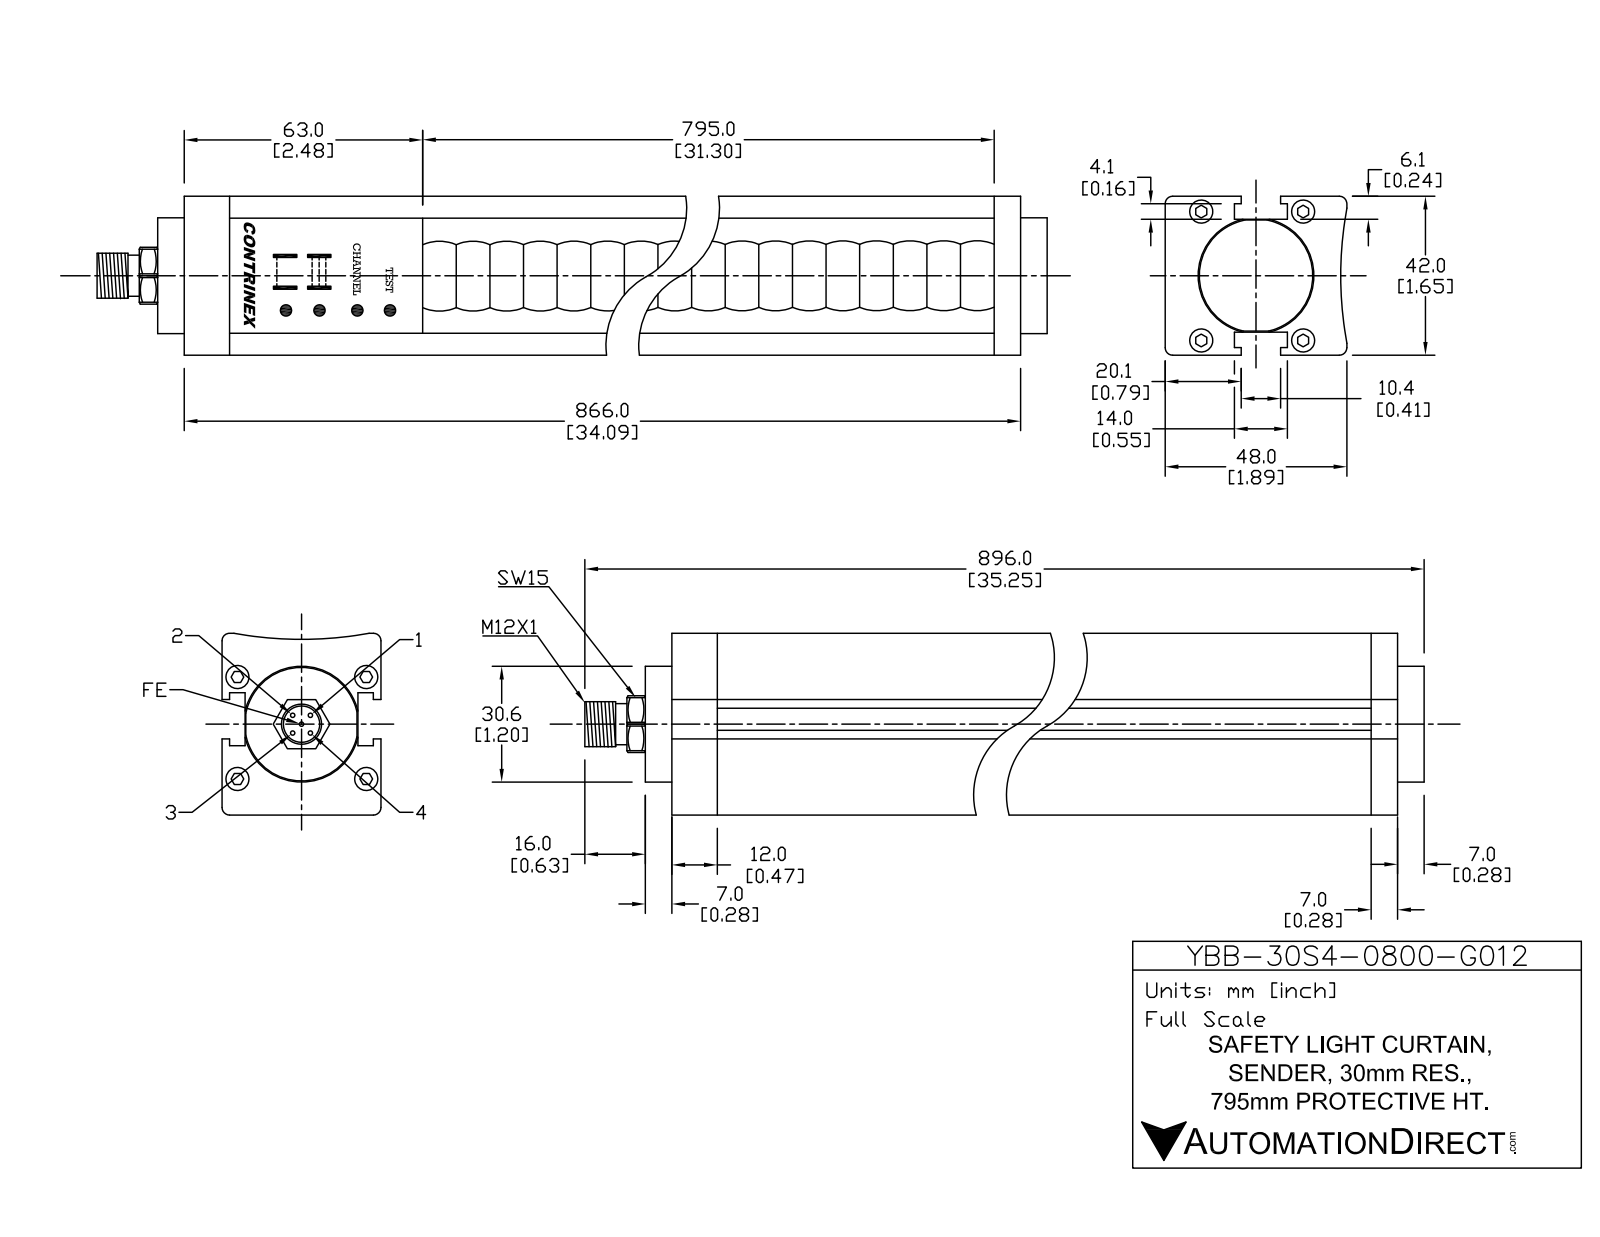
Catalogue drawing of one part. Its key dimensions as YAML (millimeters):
part_name: "YBB-30S4-0800-G012"
step_written_by: "SolidWorks 2016 (AUTOMOTIVE_DESIGN)"
units: millimeters
bodies: {solids: 19, faces: 440, planar: 208, cylindrical: 168, other: 64}
overall_size: [896, 48, 42]
volume: 1561000
surface_area: 202395
round_holes:
  - {diameter: 6, count: 4}
  - {diameter: 8.5, count: 1}
  - {diameter: 32, count: 1}
round_bosses_or_shafts:
  - {diameter: 1, count: 5}
  - {diameter: 5.5, count: 4}
  - {diameter: 30.6, count: 1}
  - {diameter: 12, count: 1}
  - {diameter: 10.5, count: 1}
partial_cylinders:
  - {radius: 1, count: 48}
  - {radius: 0.5, count: 4}
  - {radius: 0.55, count: 2}
  - {radius: 8.2, count: 1}
  - {radius: 100, count: 1}
face_to_face_distances: [6.3, 35.7, 42, 29.4, 14, 17.2, 31.2, 15.7, 29.7, 46.9]
hole_center_spacings: [21.04, 22.34, 26.9, 34, 43.35]
